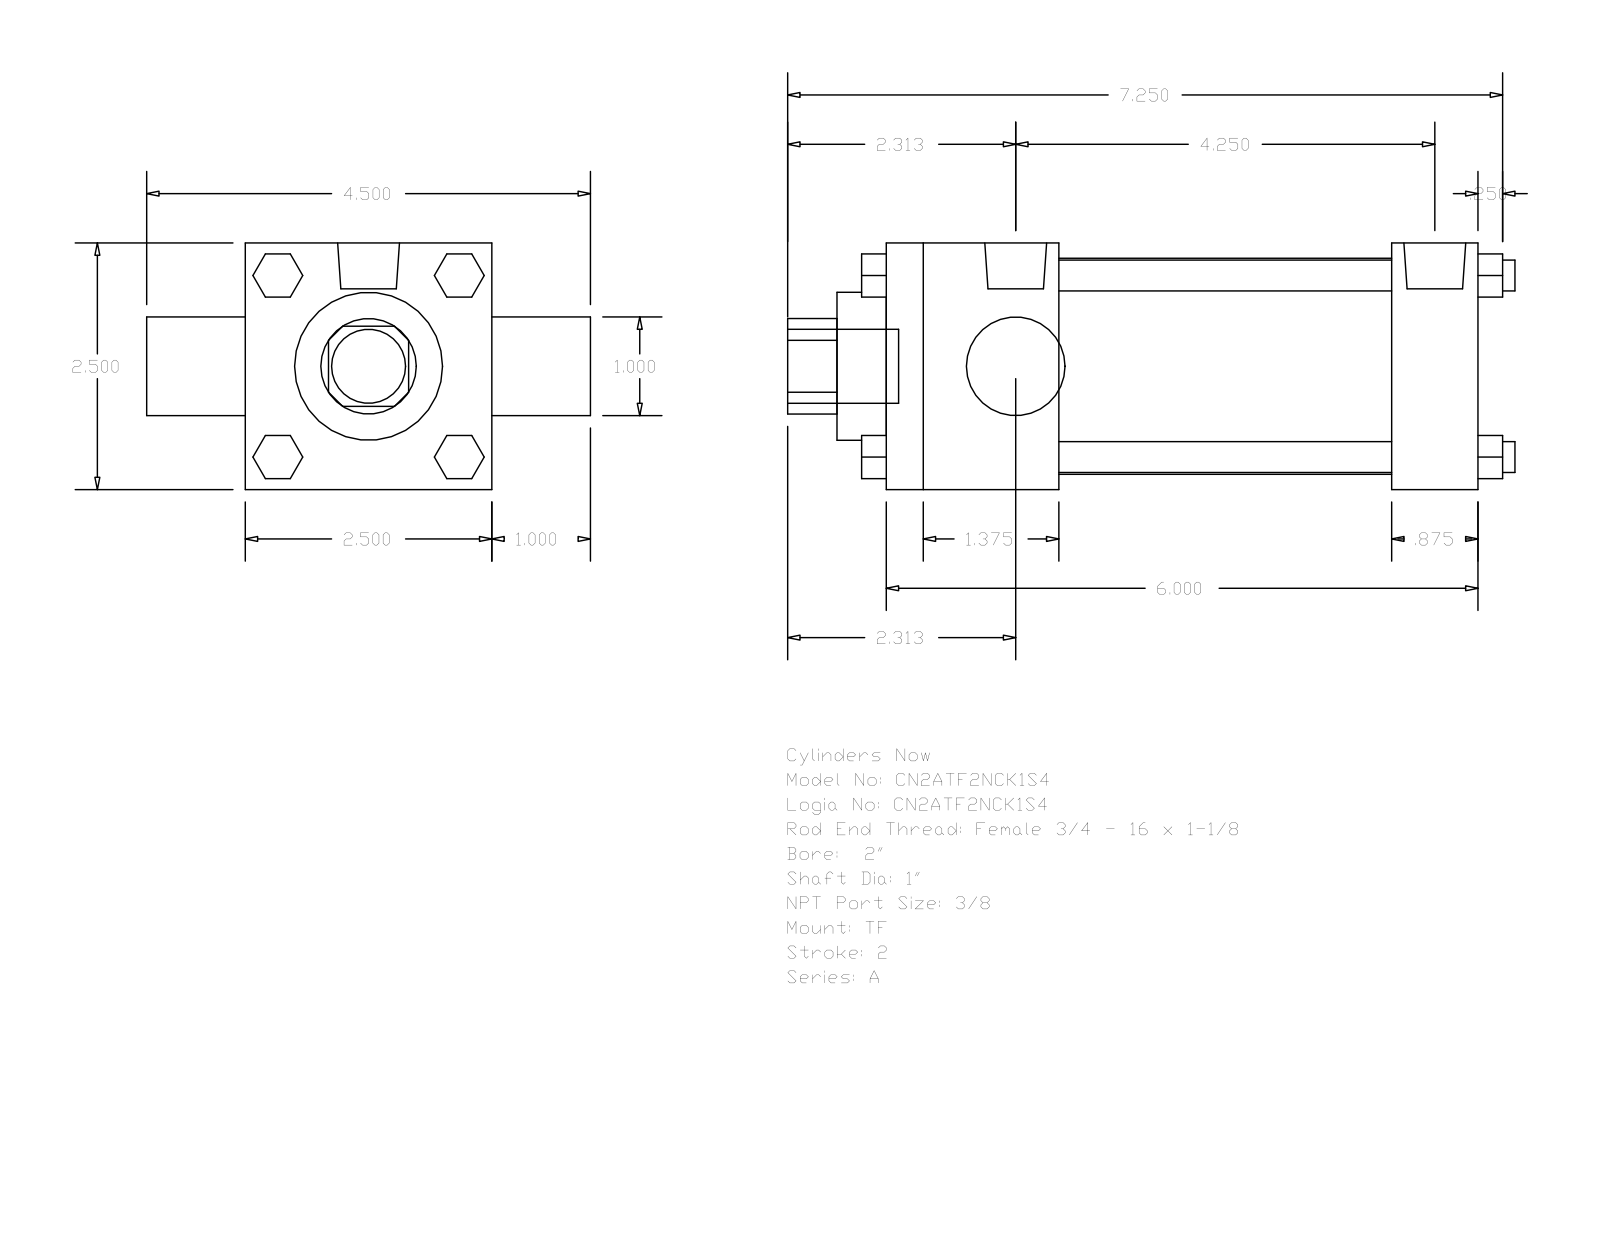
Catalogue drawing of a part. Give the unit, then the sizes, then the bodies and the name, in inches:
Units: inches
Overall size (bounding box): 7.375 × 4.5 × 2.5
Round holes (diameter × count): ⌀1 ×2, ⌀1.5 ×1, ⌀2.19 ×1
Round bosses / shafts (diameter × count): ⌀0.313 ×4, ⌀0.219 ×3, ⌀0.627 ×2, ⌀0.75 ×1
Partial cylindrical surfaces — rounded edges, fillets, slot ends (radius × count): R0.484 ×1
Main face-to-face distances: 2.5, 6, 1.75, 5.125, 3.375, 4.25, 0.875, 1, 3.5, 6.5
Bodies: 0 solids, 120 faces (92 planar, 28 cylindrical, 0 other)
Part name (STEP PRODUCT): A_TF__0200_1
STEP written by: GSSL Pune (CONFIG_CONTROL_DESIGN)
